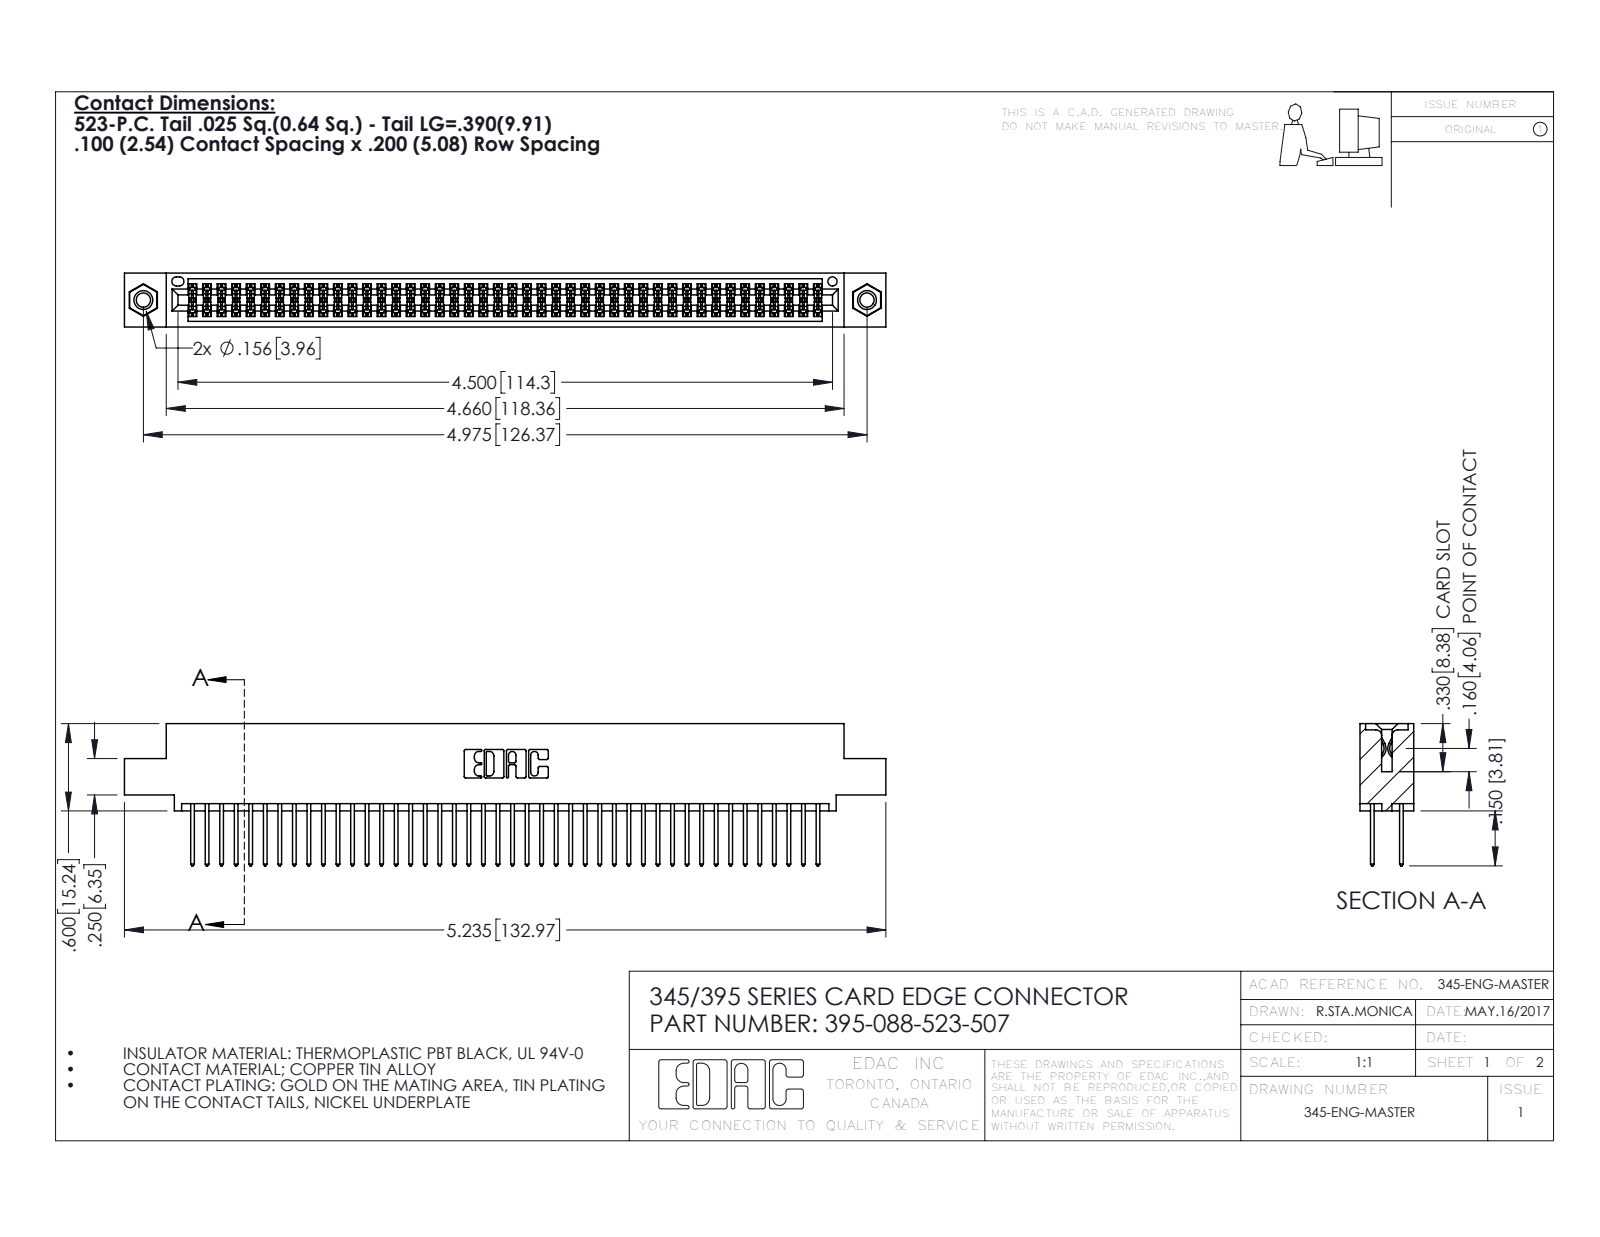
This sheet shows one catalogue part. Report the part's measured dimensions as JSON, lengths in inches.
{"part_name": "345 Part_0.110 Offset - 0.156 Dia-TI; 395-088-523-507; 345-292-001_345-293-123; 345-250-001_345-250-005-103", "step_written_by": "SolidWorks 2016 (CONFIG_CONTROL_DESIGN)", "units": "inches", "bodies": {"solids": 91, "faces": 4590, "planar": 3020, "cylindrical": 1554, "other": 16}, "overall_size": [5.235, 0.977, 0.37], "volume_in3": 0.795, "surface_area_in2": 31.35, "round_holes": [[0.098, 2], [0.125, 2], [0.156, 2], [0.064, 1]], "round_bosses_or_shafts": [[0.155, 2]], "partial_cylinders_radius": [[0.006, 132], [0.01, 88], [0.01, 22], [0.007, 6], [0.031, 6], [0.026, 3], [0.014, 2], [0.019, 2]], "face_to_face_distances": [0.072, 0.298, 0.2, 0.098, 0.272, 0.025, 0.37, 0.225, 0.175, 0.149], "hole_center_spacings": [0.27, 4.739, 4.975]}
